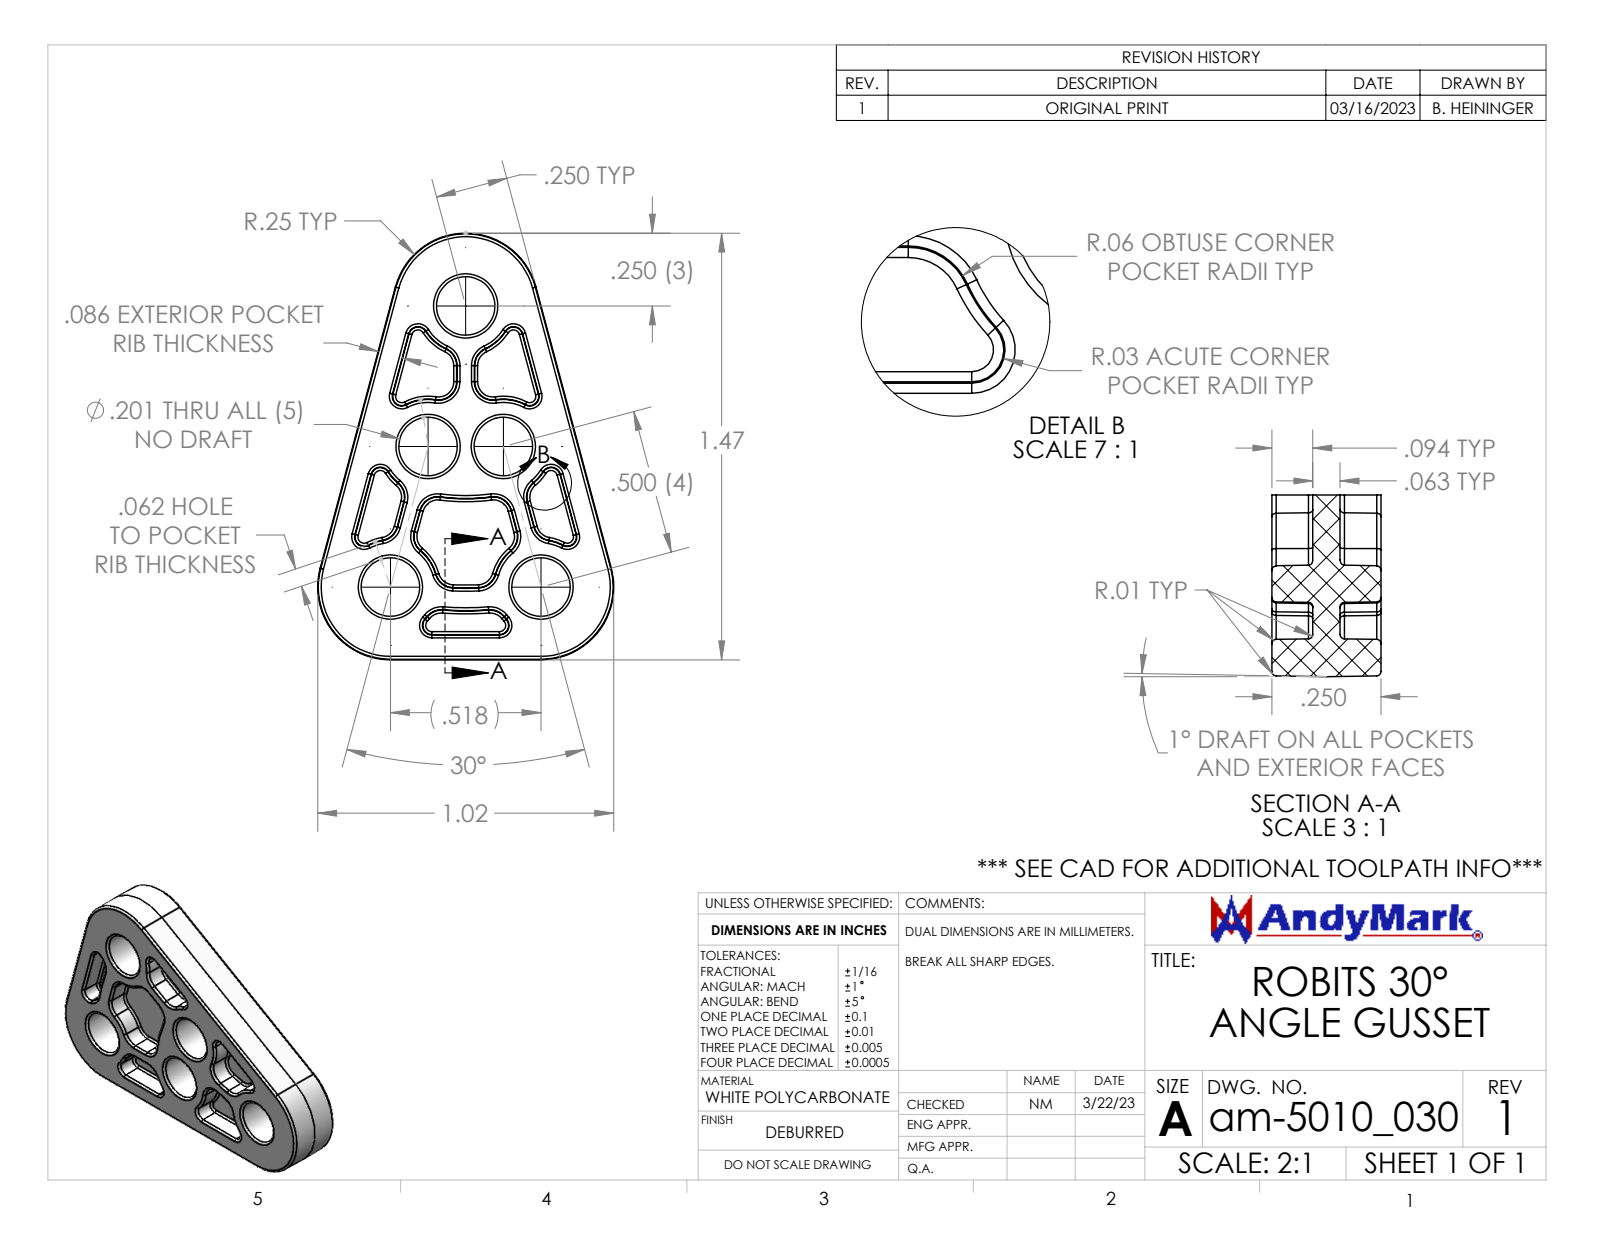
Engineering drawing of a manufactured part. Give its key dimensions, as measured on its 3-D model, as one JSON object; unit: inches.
{"part_name": "am-5010_030 RoBits Angle Gusset (30°)", "step_written_by": "SolidWorks 2022 (AUTOMOTIVE_DESIGN)", "units": "inches", "bodies": {"solids": 1, "faces": 432, "planar": 42, "cylindrical": 60, "other": 330}, "overall_size": [1.5, 1, 0.25], "volume_in3": 0.18, "surface_area_in2": 4.367, "round_holes": [[0.201, 5]], "partial_cylinders_radius": [[0.01, 42]], "face_to_face_distances": [0.25, 0.094, 0.156, 0.062, 0.087, 0.088, 0.064, 0.218, 0.131, 0.282], "hole_center_spacings": [0.5, 0.62, 1, 0.259, 0.518]}
